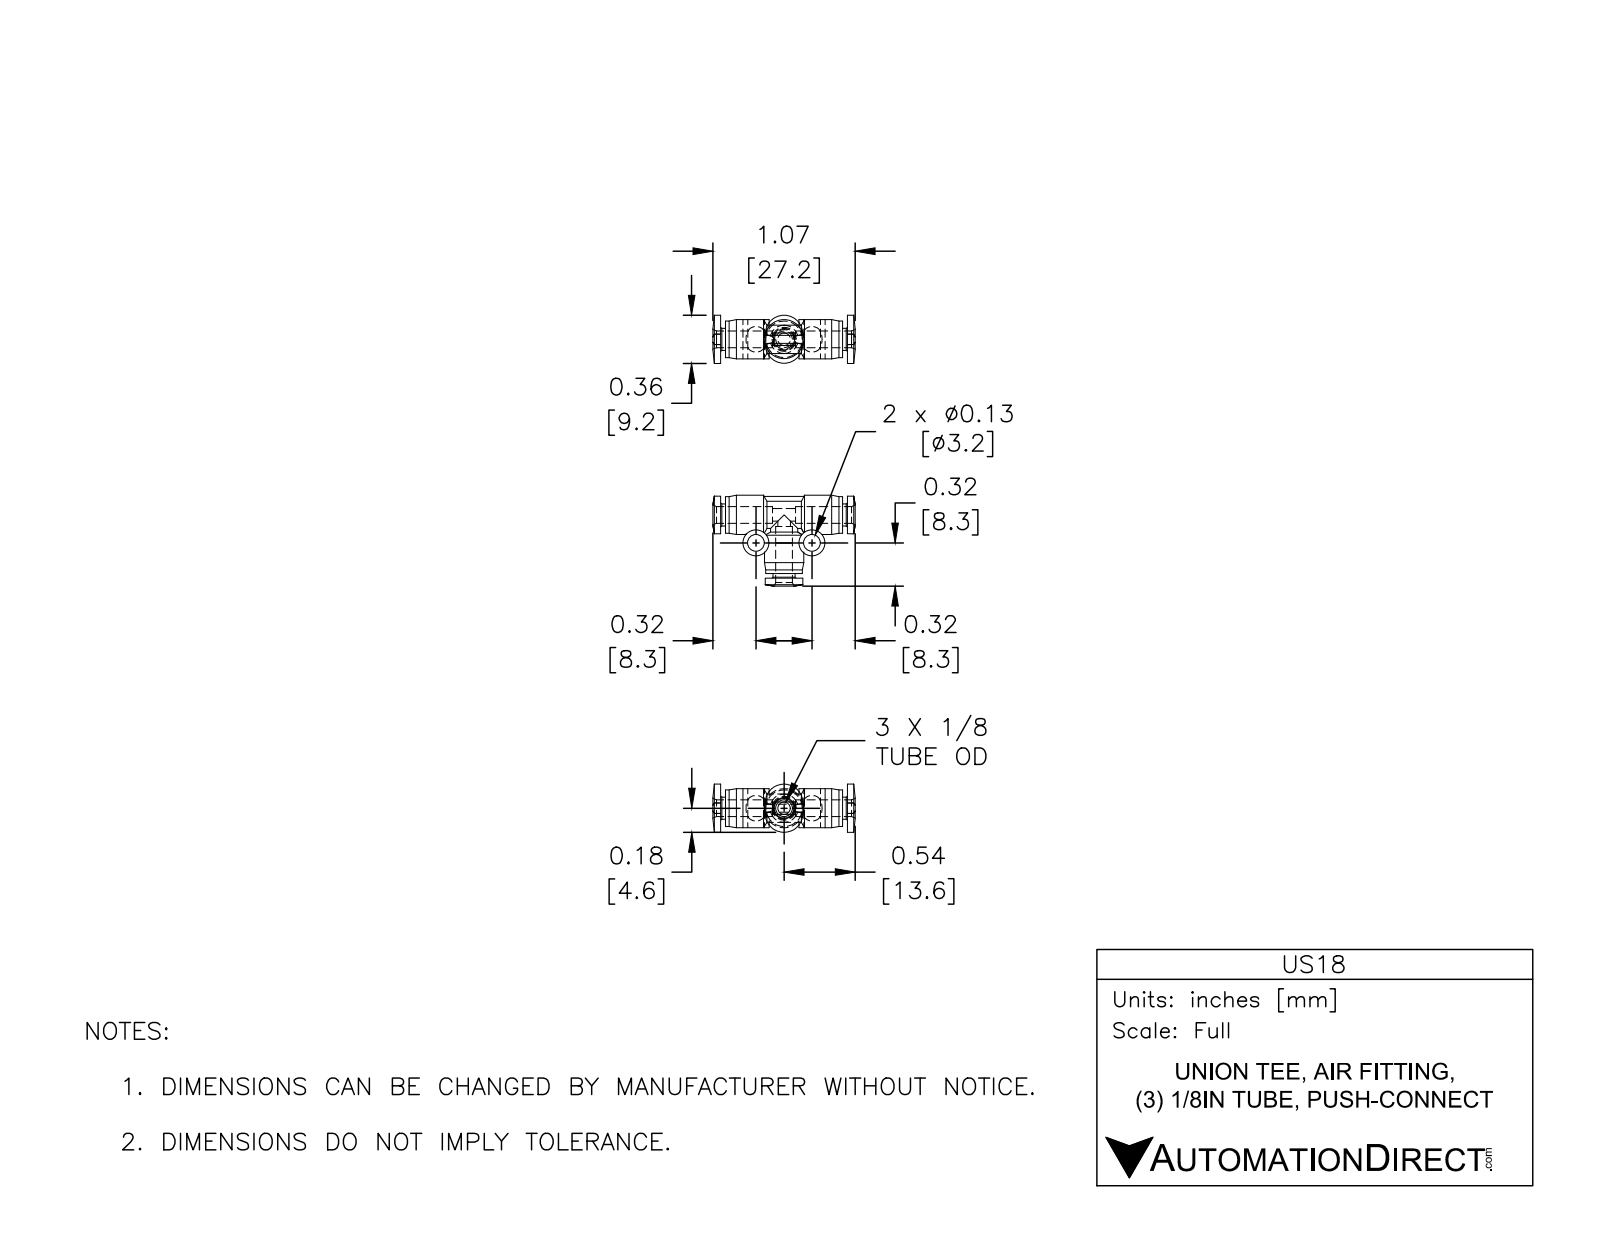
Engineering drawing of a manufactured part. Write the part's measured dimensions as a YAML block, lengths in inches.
part_name: "UT18"
step_written_by: "SolidWorks 2015 (CONFIG_CONTROL_DESIGN)"
units: inches
bodies: {solids: 1, faces: 120, planar: 29, cylindrical: 52, other: 39}
overall_size: [1.071, 0.683, 0.362]
volume: 0.079
surface_area: 2.884
round_holes:
  - {diameter: 0.126, count: 4}
  - {diameter: 0.094, count: 2}
round_bosses_or_shafts:
  - {diameter: 0.295, count: 2}
  - {diameter: 0.276, count: 2}
  - {diameter: 0.213, count: 2}
  - {diameter: 0.197, count: 2}
  - {diameter: 0.165, count: 2}
partial_cylinders:
  - {radius: 0.142, count: 4}
face_to_face_distances: [0.035, 0.917, 0.953, 0.882, 0.295, 0.118, 0.177, 0.059, 0.616, 0.581]
hole_center_spacings: [0.421]
